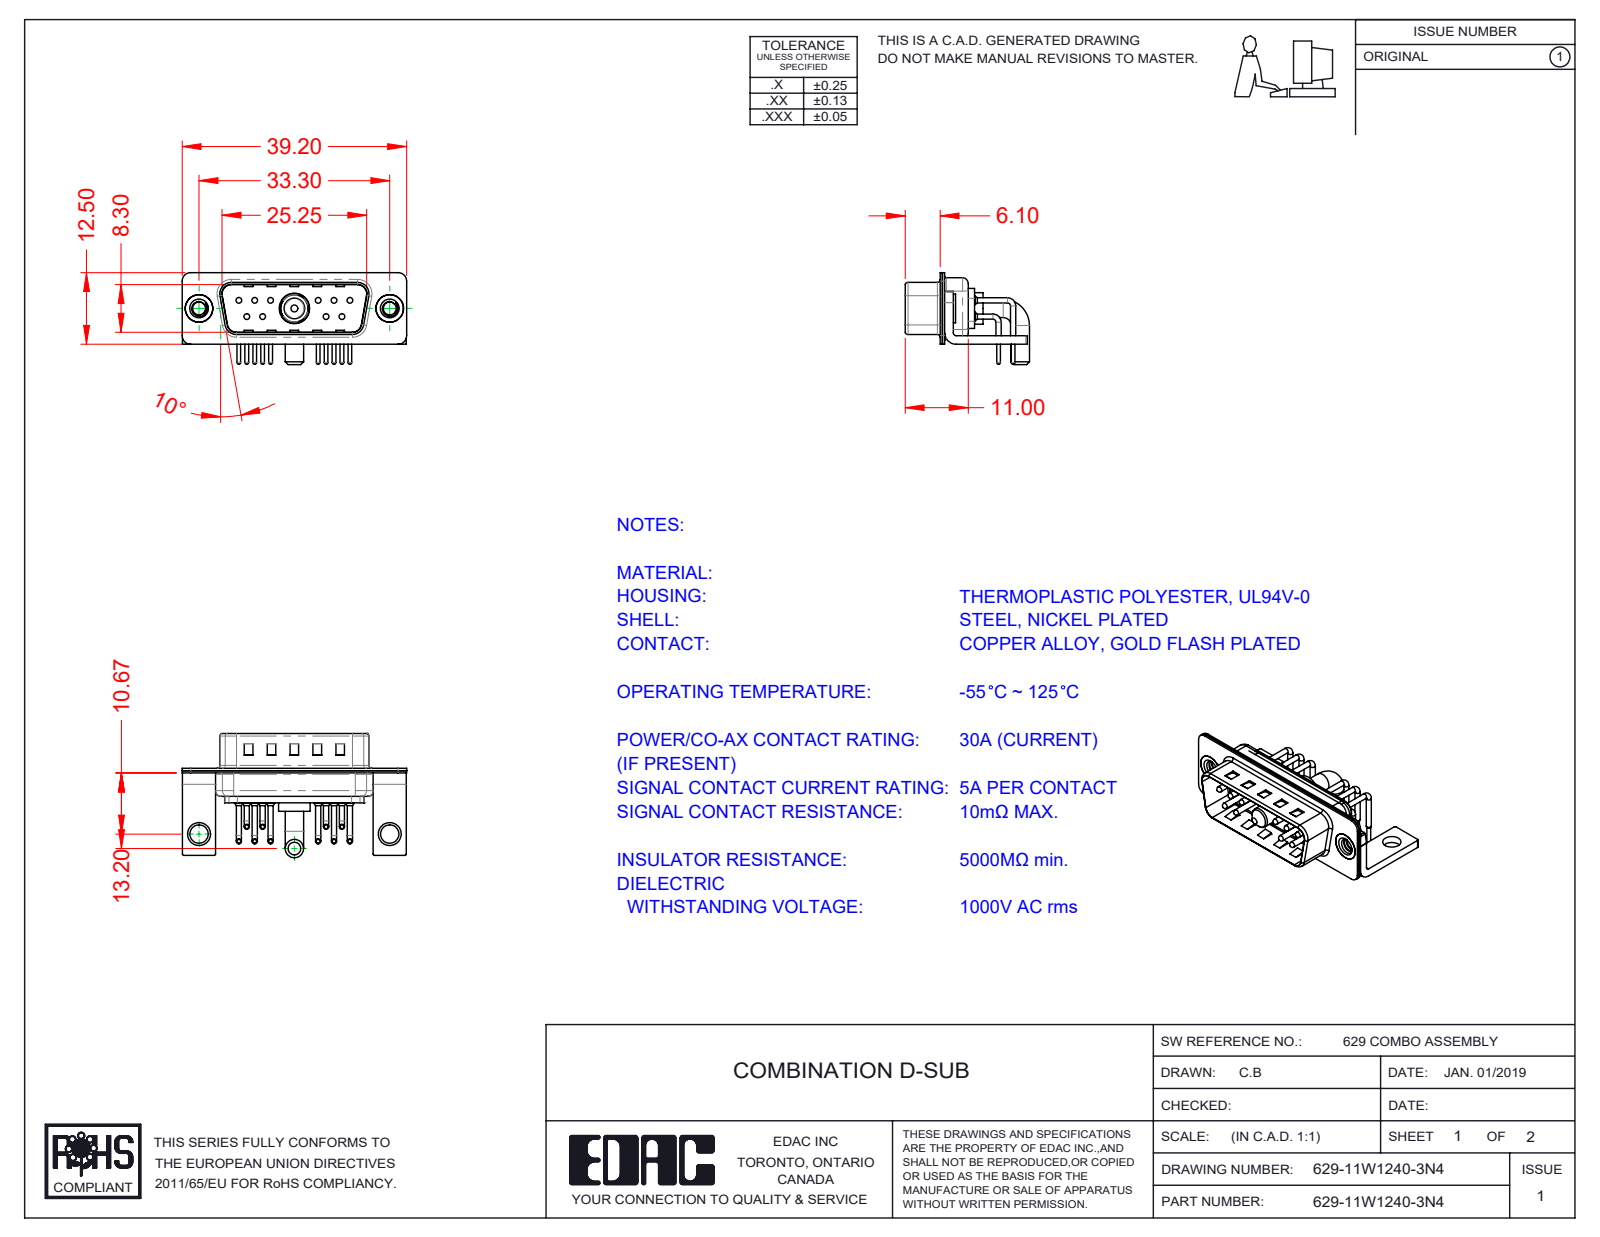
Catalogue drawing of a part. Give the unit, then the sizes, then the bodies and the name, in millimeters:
Units: millimetres
Overall size (bounding box): 39.2 × 21.7 × 16.05
Round holes (diameter × count): ⌀0.75 ×10, ⌀1.6 ×10, ⌀2 ×10, ⌀2.26 ×2, ⌀3.2 ×2, ⌀4 ×2, ⌀4.8 ×2, ⌀4.85 ×1, ⌀5.3 ×1
Round bosses / shafts (diameter × count): ⌀0.9 ×20, ⌀1.5 ×10, ⌀1 ×10, ⌀0.65 ×10, ⌀5 ×2, ⌀4.9 ×2, ⌀3.2 ×2, ⌀5.5 ×1
Partial cylindrical surfaces — rounded edges, fillets, slot ends (radius × count): R0.25 ×16, R1.5 ×16, R2 ×13, R1.01 ×10, R0.5 ×9, R1.6 ×8, R1 ×7, R0.6 ×4
Main face-to-face distances: 0.4, 0.8, 1.5, 9.5, 9.1, 8.7, 9.9, 0.6, 1.9, 5.2
Hole centre spacings: 3.16, 2.77, 13.85, 11.08, 16.62, 5.03, 5.04, 5.54
Volume: 2 359 mm³ · Surface area: 5 838 mm²
Bodies: 19 solids, 1536 faces (818 planar, 536 cylindrical, 182 other)
Part name (STEP PRODUCT): 629Combo Contact Row 1; 629Combo Threaded Rivet_3; 629Combo Shell Front_15 Contacts; 629-11W1240-3N4 (+5 more)
STEP written by: SolidWorks 2020 (CONFIG_CONTROL_DESIGN)
